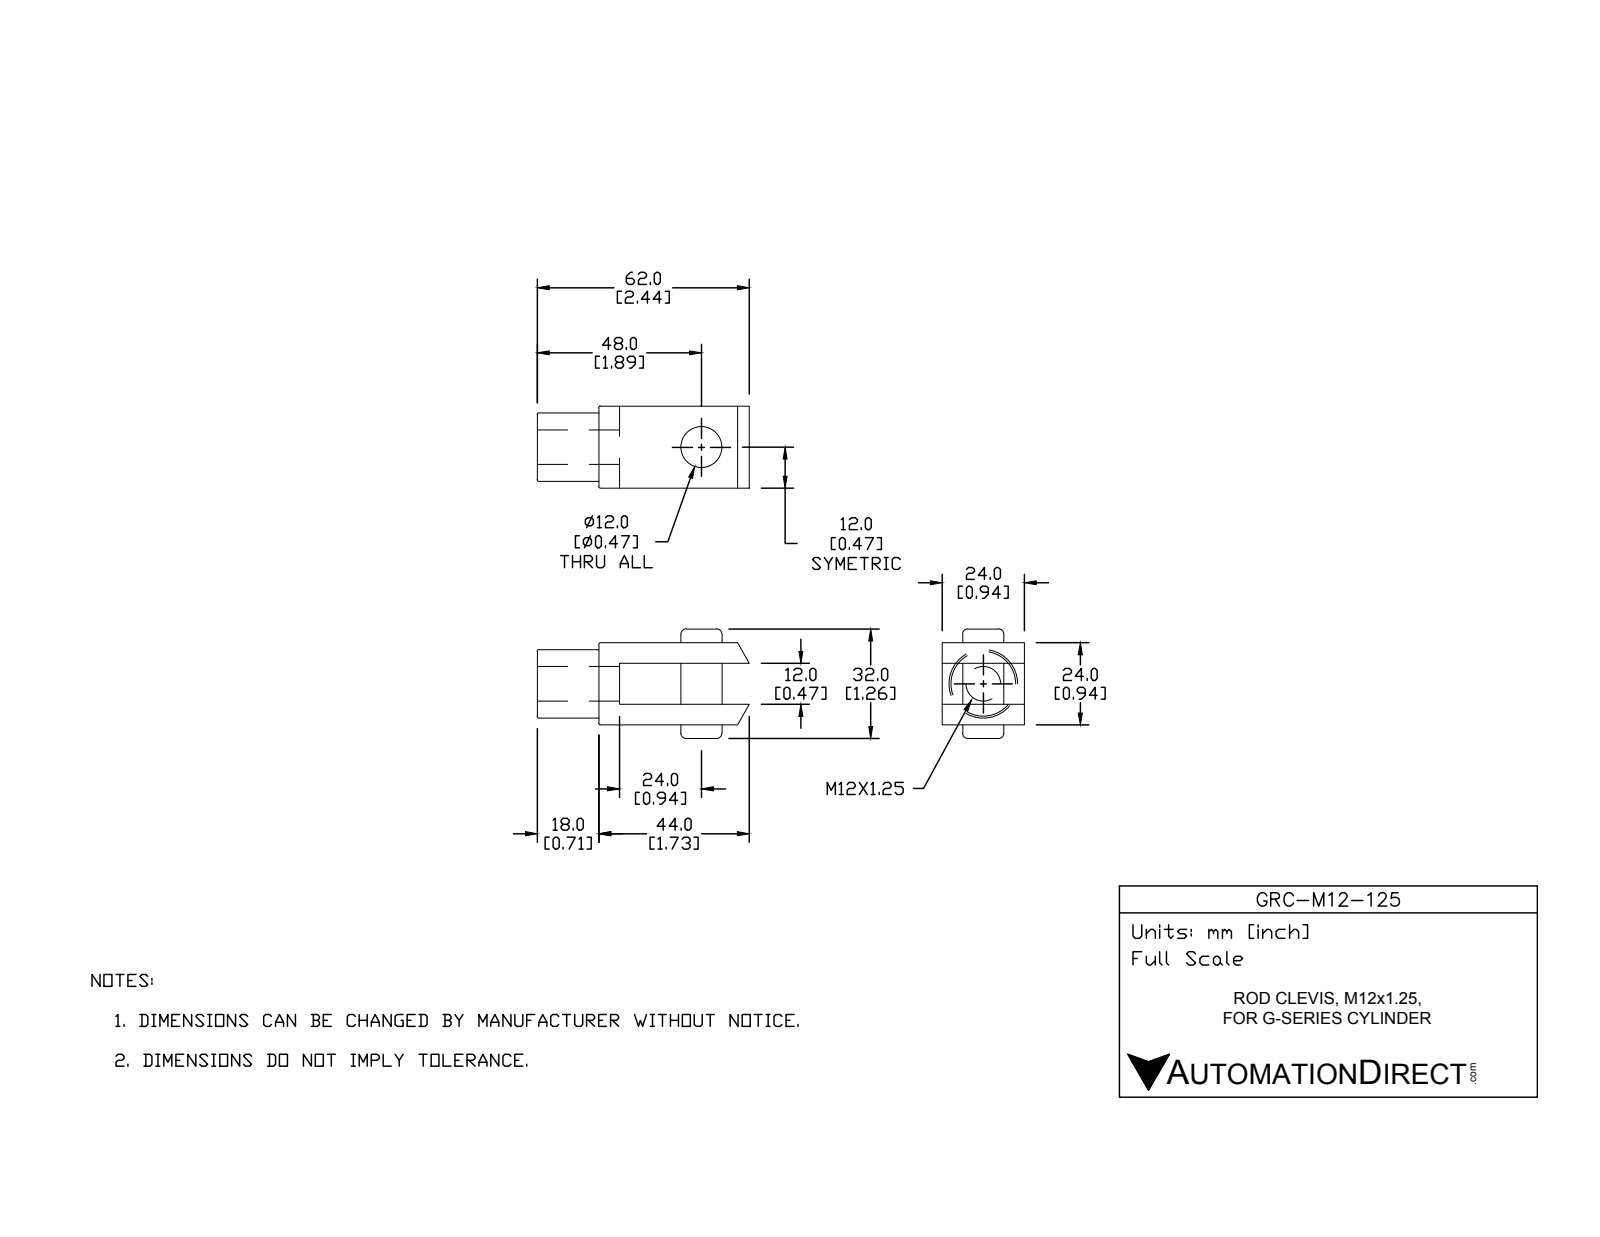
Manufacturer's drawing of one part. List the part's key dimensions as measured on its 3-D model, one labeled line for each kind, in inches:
Part name (STEP PRODUCT): GRC-M12-125
STEP written by: SolidWorks 2017 (AUTOMOTIVE_DESIGN)
Units: inches
Bodies: 1 solid, 33 faces (13 planar, 14 cylindrical, 6 other)
Overall size (bounding box): 2.441 × 1.26 × 0.945
Volume: 1.172 in³ · Surface area: 12.78 in²
Round holes (diameter × count): ⌀0.425 ×1
Round bosses / shafts (diameter × count): ⌀0.787 ×1, ⌀0.472 ×1
Partial cylindrical surfaces — rounded edges, fillets, slot ends (radius × count): R0.039 ×4
Main face-to-face distances: 0.236, 0.709, 0.945, 0.472, 0.157, 0.394, 0.866, 1.102, 1.26
